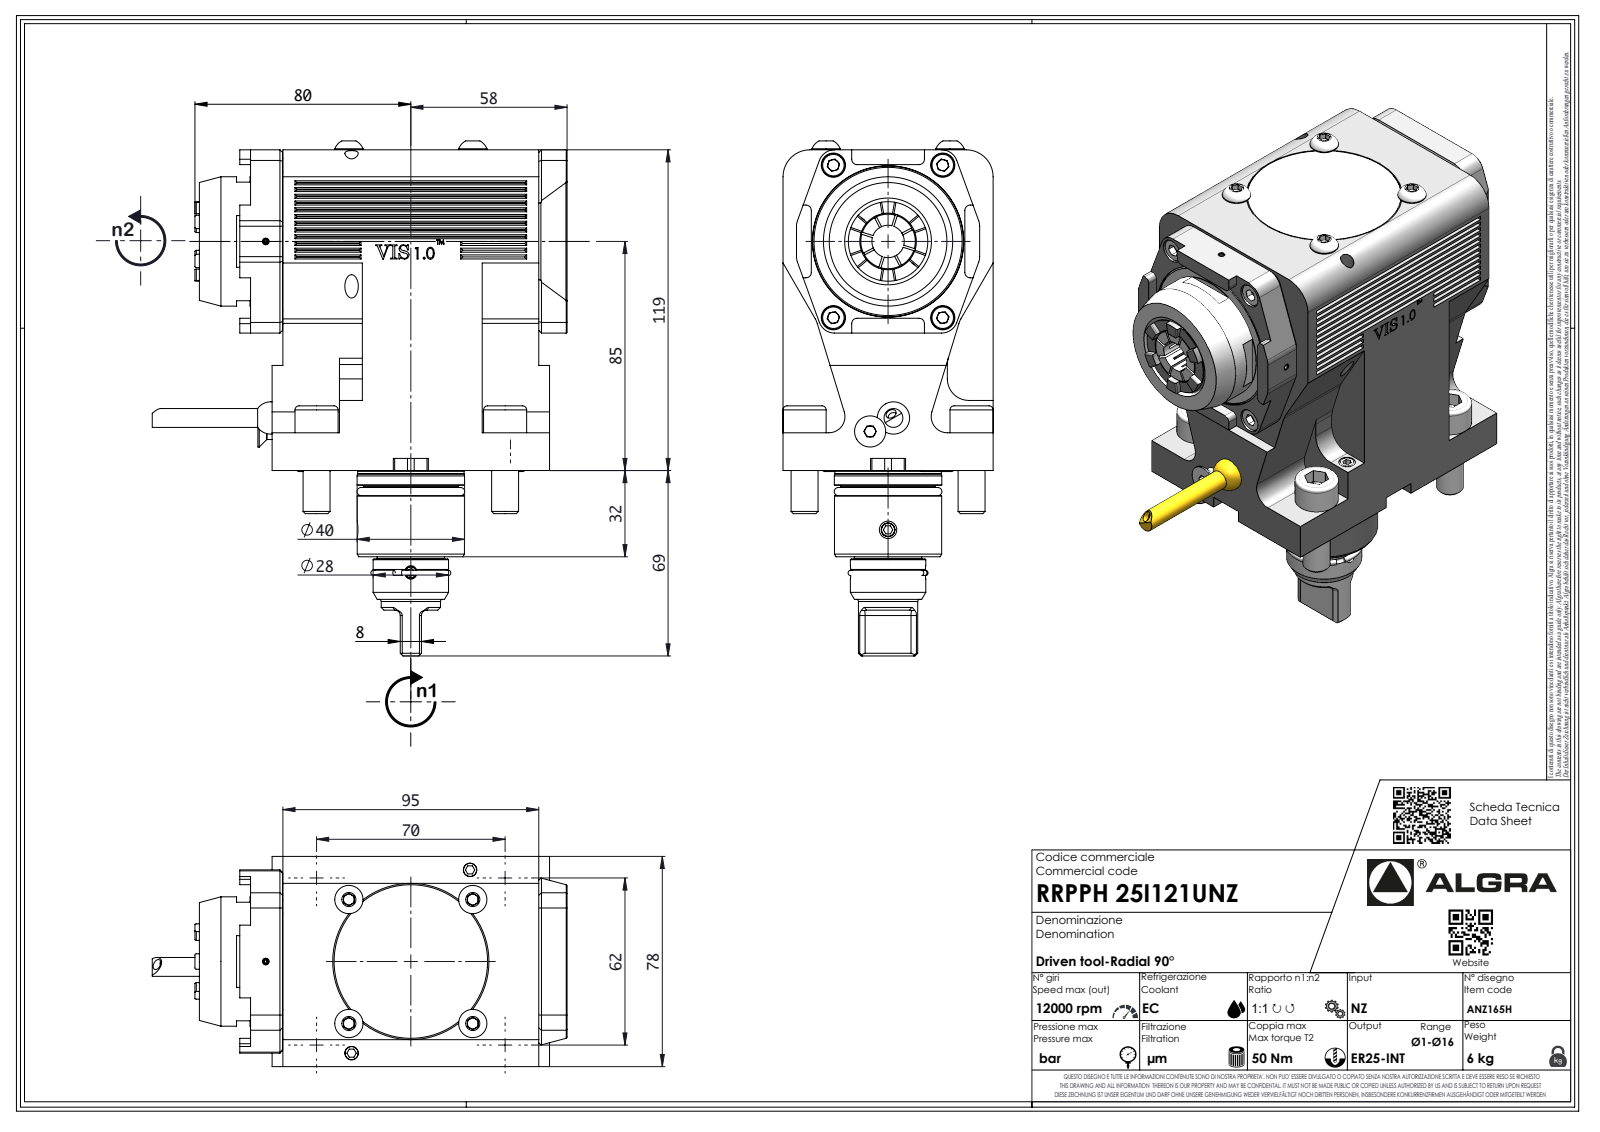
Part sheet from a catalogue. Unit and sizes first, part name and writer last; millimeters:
Units: millimetres
Overall size (bounding box): 187.8 × 143.65 × 78
Round holes (diameter × count): ⌀2.1 ×1, ⌀6 ×1
Round bosses / shafts (diameter × count): ⌀16 ×4, ⌀10 ×4, ⌀48 ×1, ⌀39.9 ×1, ⌀39.8 ×1, ⌀39.5 ×1, ⌀35.1 ×1, ⌀35 ×1
Partial cylindrical surfaces — rounded edges, fillets, slot ends (radius × count): R5 ×16, R2 ×14, R6 ×10, R0.33 ×7, R0.52 ×7, R3.7 ×7, R8 ×6, R35 ×6
Main face-to-face distances: 78, 119, 4, 12, 99, 106, 25, 106.1, 111, 21
Volume: 998 532 mm³ · Surface area: 87 751 mm²
Bodies: 1 solid, 647 faces (393 planar, 131 cylindrical, 123 other)
Part name (STEP PRODUCT): RRPPH25I121UNZ
STEP written by: SolidWorks 2023 (AUTOMOTIVE_DESIGN)
